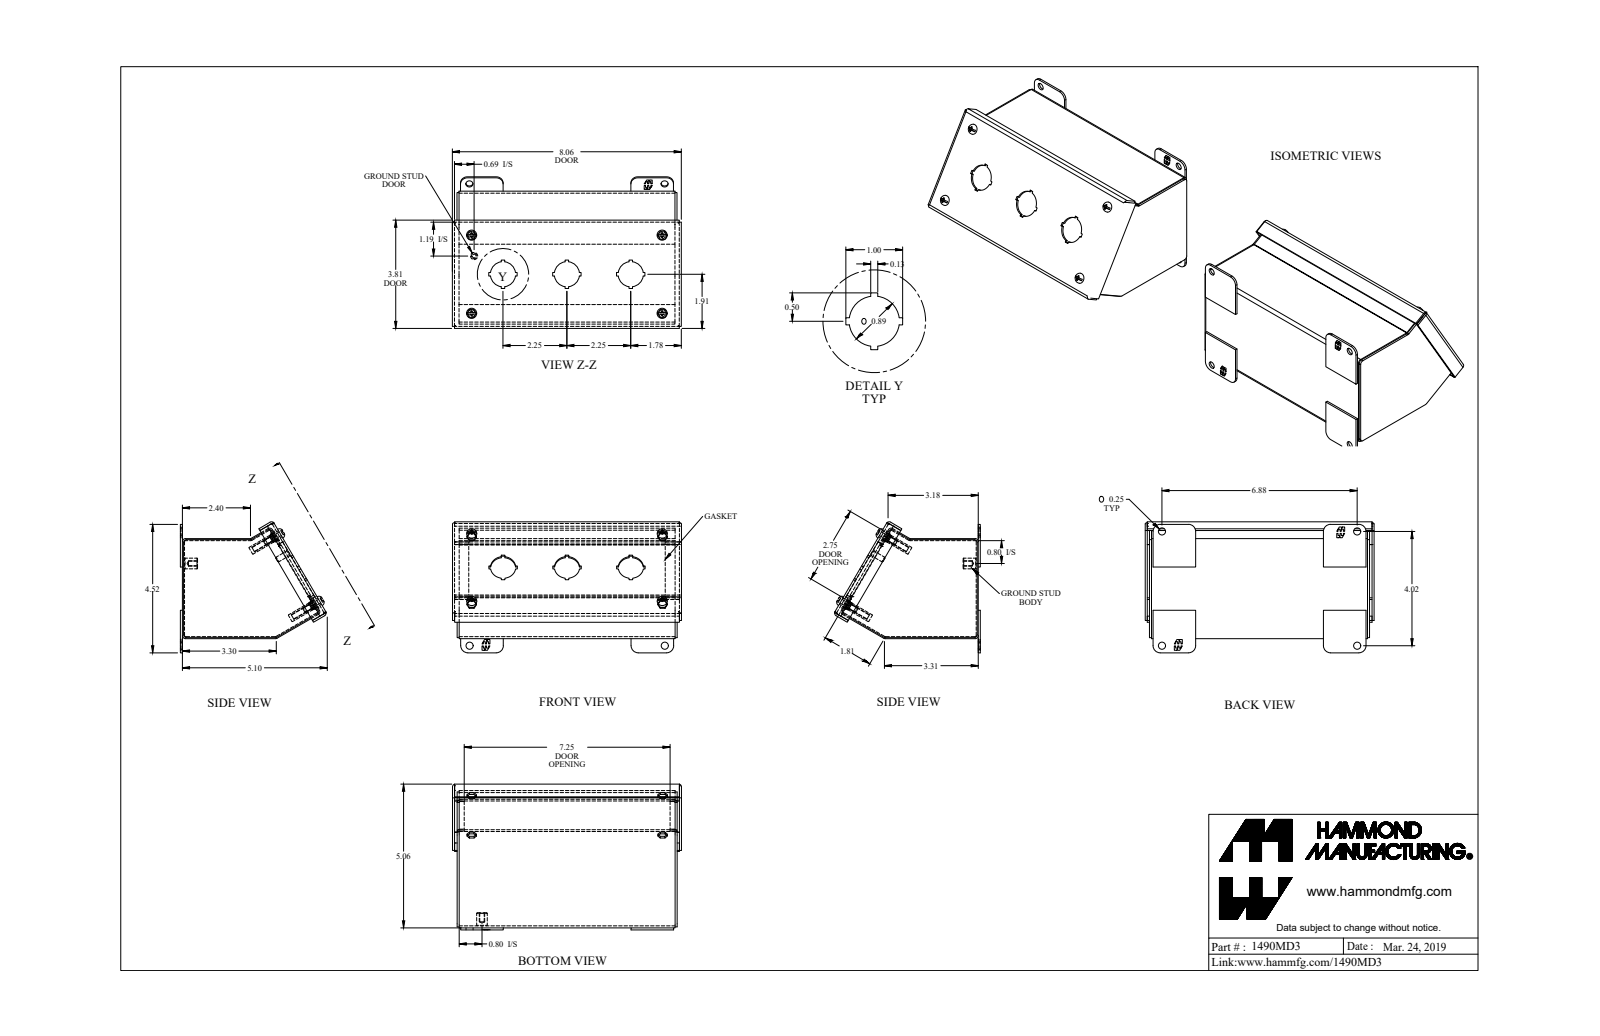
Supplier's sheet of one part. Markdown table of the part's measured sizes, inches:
| quantity | value |
| --- | --- |
| part name | 1490MD3_Default |
| STEP written by | SolidWorks 2019 (CONFIG_CONTROL_DESIGN) |
| units | inches |
| bodies | 21 solids, 644 faces (454 planar, 152 cylindrical, 38 other) |
| overall size | 8.062 × 5.176 × 4.635 |
| volume | 12.84 in³ |
| surface area | 369.5 in² |
| round holes (diameter × count) | 0.25 × 8, 0.159 × 4, 0.875 × 3, 0.156 × 1 |
| round bosses / shafts (diameter × count) | 0.39 × 4, 0.275 × 4, 0.19 × 4, 0.148 × 4, 0.375 × 1 |
| partial cylindrical surfaces (radius × count) | 0.108 × 18, 0.036 × 12, 0.25 × 8, 0.125 × 4, 0.16 × 4, 0.171 × 4 |
| main face-to-face distances | 0.072, 3.45, 0.072, 7.678, 3.522, 3.378, 7.606, 7.75, 3.428, 0.221 |
| hole center spacings | 6.71, 6.724, 1.764, 2.25, 2.75, 2.751, 2.756, 3.626 |
